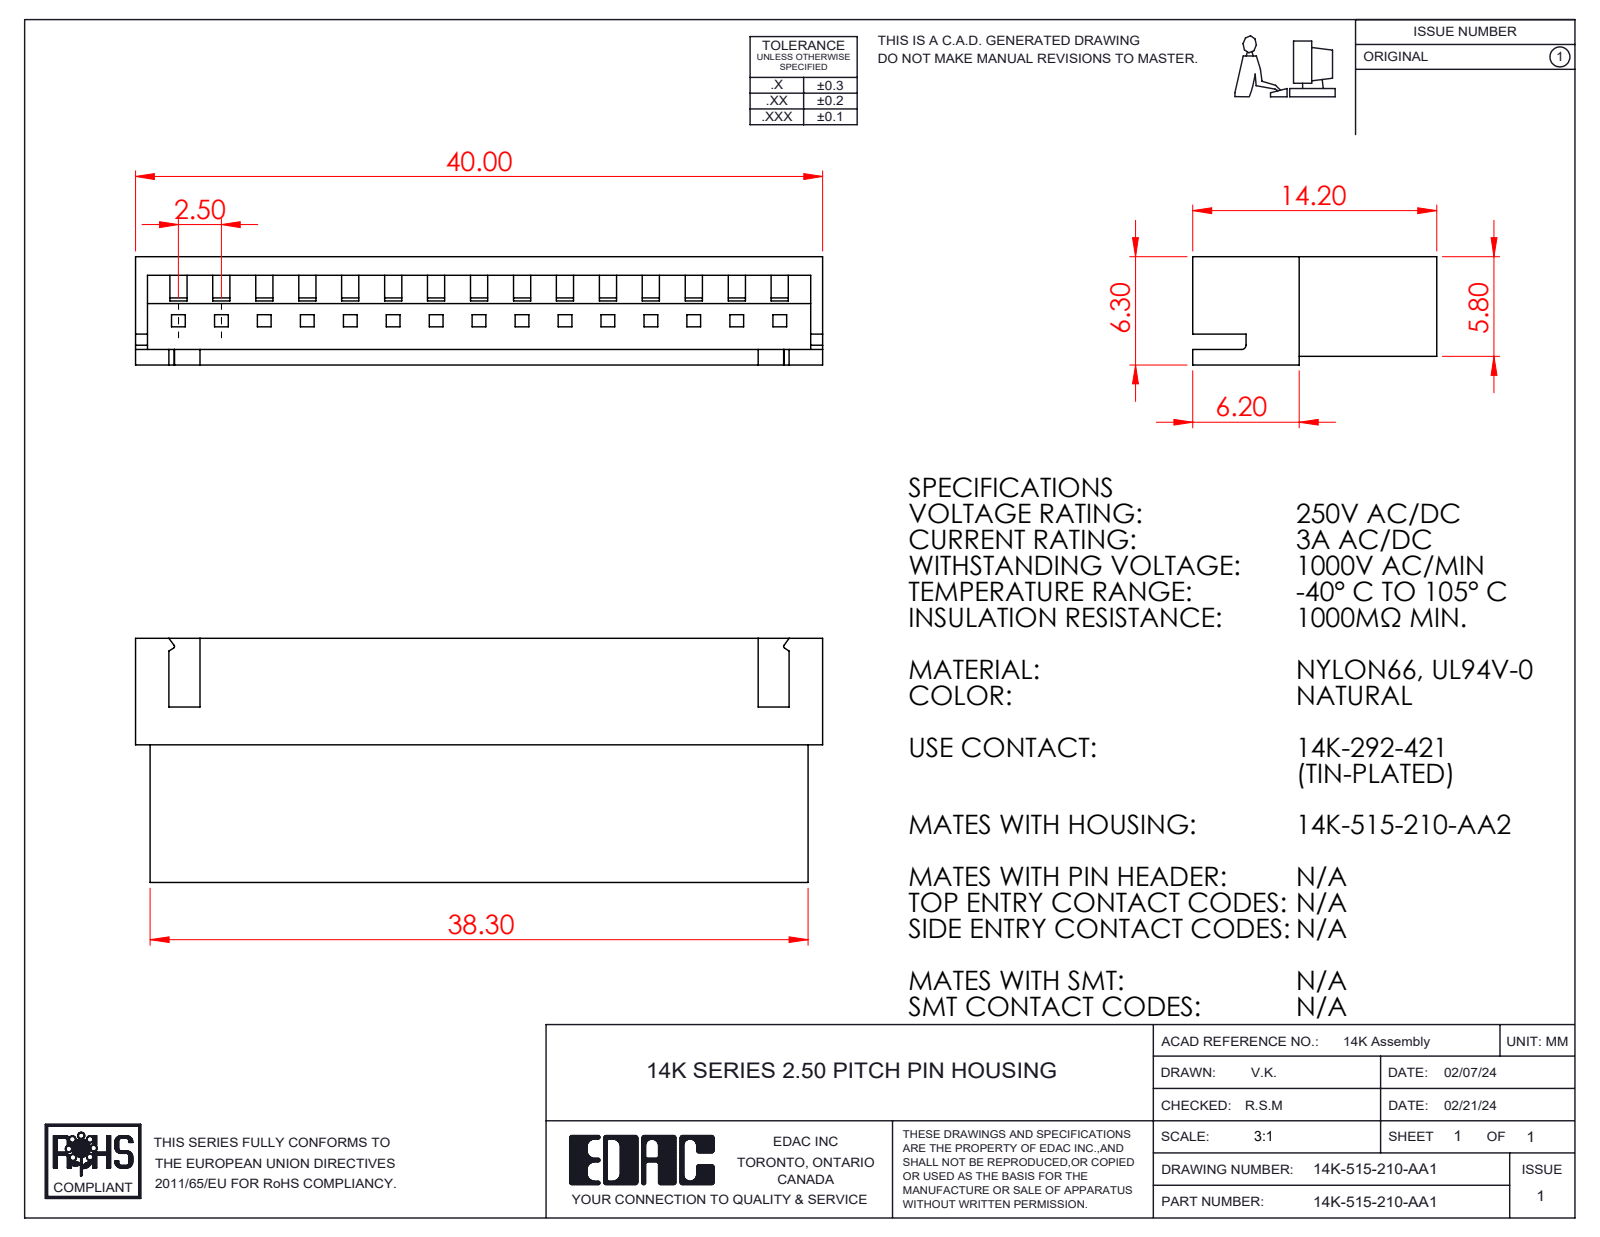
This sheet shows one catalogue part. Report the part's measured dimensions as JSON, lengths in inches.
{"part_name": "14K-515-210-AA1", "step_written_by": "SolidWorks 2023 (CONFIG_CONTROL_DESIGN)", "units": "inches", "bodies": {"solids": 1, "faces": 414, "planar": 410, "cylindrical": 4, "other": 0}, "overall_size": [1.575, 0.559, 0.248], "volume_in3": 0.105, "surface_area_in2": 5.958, "partial_cylinders_radius": [[0.004, 2], [0.01, 1]], "face_to_face_distances": [0.098, 0.02, 0.035, 0.228, 0.197, 0.295, 0.193, 0.394, 0.134, 0.154]}
